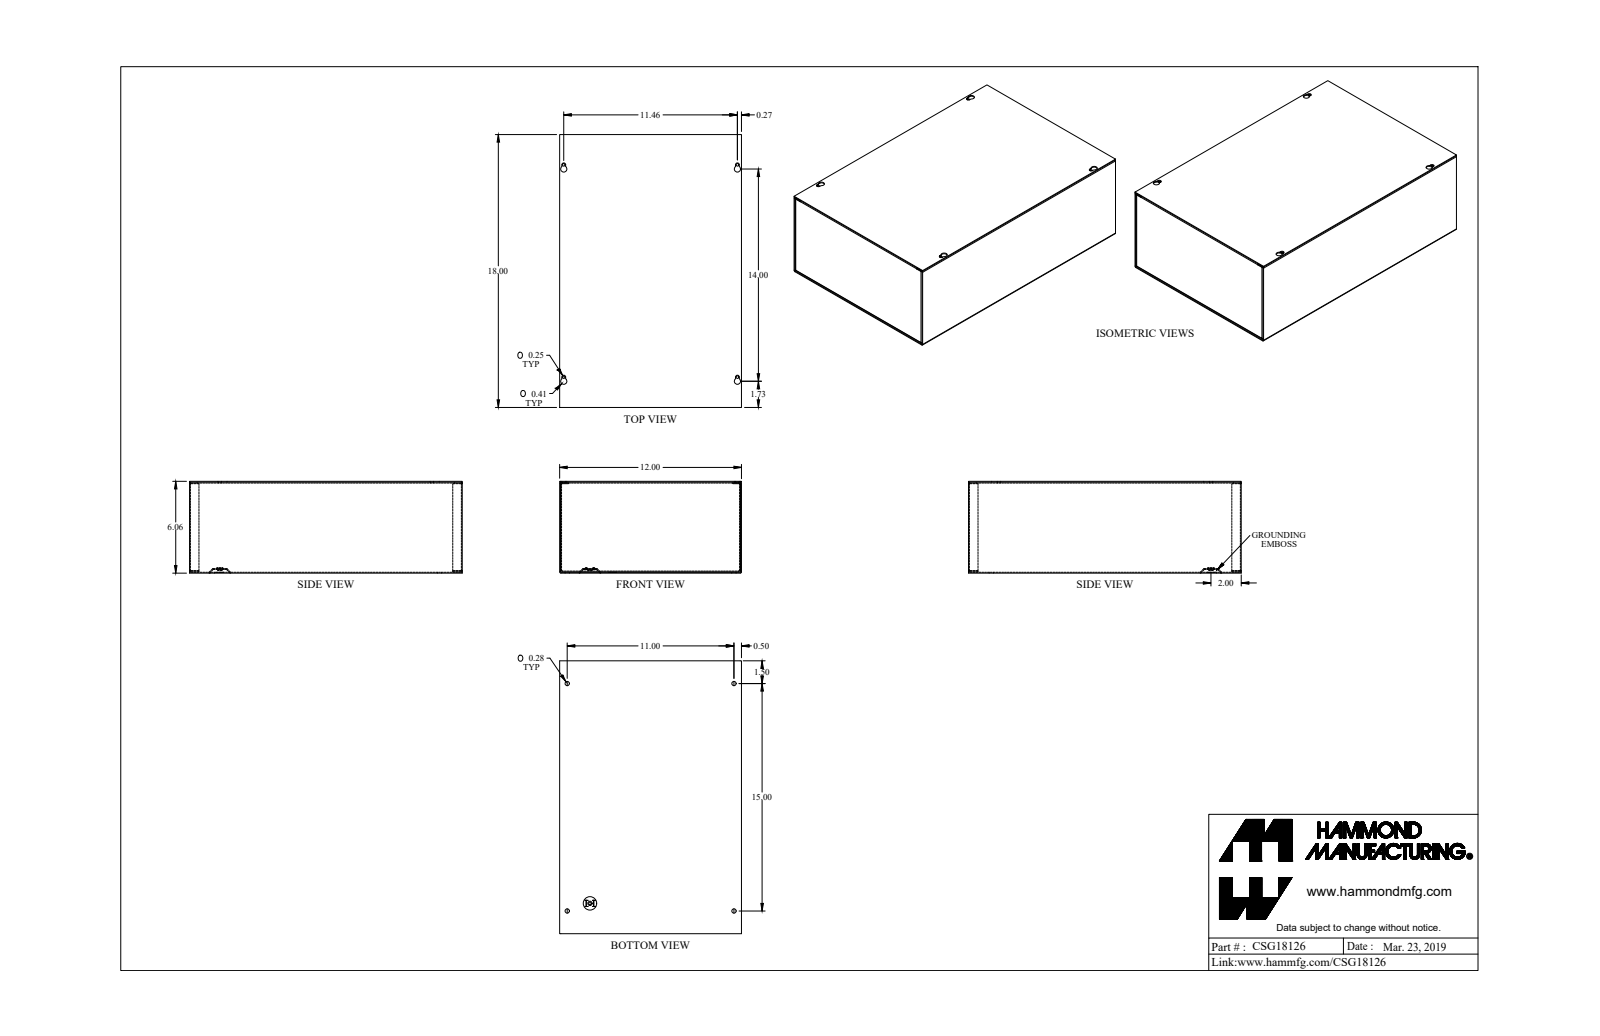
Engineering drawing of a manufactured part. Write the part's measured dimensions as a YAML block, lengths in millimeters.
part_name: "CSG18126_Default"
step_written_by: "SolidWorks 2019 (CONFIG_CONTROL_DESIGN)"
units: millimeters
bodies: {solids: 4, faces: 205, planar: 125, cylindrical: 72, other: 8}
overall_size: [457.2, 304.8, 153.8]
volume: 779000
surface_area: 1085000
round_holes:
  - {diameter: 4.3, count: 5}
  - {diameter: 7.1, count: 4}
  - {diameter: 12.7, count: 1}
round_bosses_or_shafts:
  - {diameter: 12.5, count: 1}
  - {diameter: 7.2, count: 1}
partial_cylinders:
  - {radius: 0.7, count: 12}
  - {radius: 2.2, count: 12}
  - {radius: 1.4, count: 8}
  - {radius: 3.2, count: 4}
  - {radius: 5.2, count: 4}
face_to_face_distances: [1.4, 152.4, 151, 153.8, 303.4, 455.8, 304.8, 301.9, 457.2, 454.3]
hole_center_spacings: [14, 285.5, 368.4, 465.8, 279.4, 291.1, 355.6, 381]
